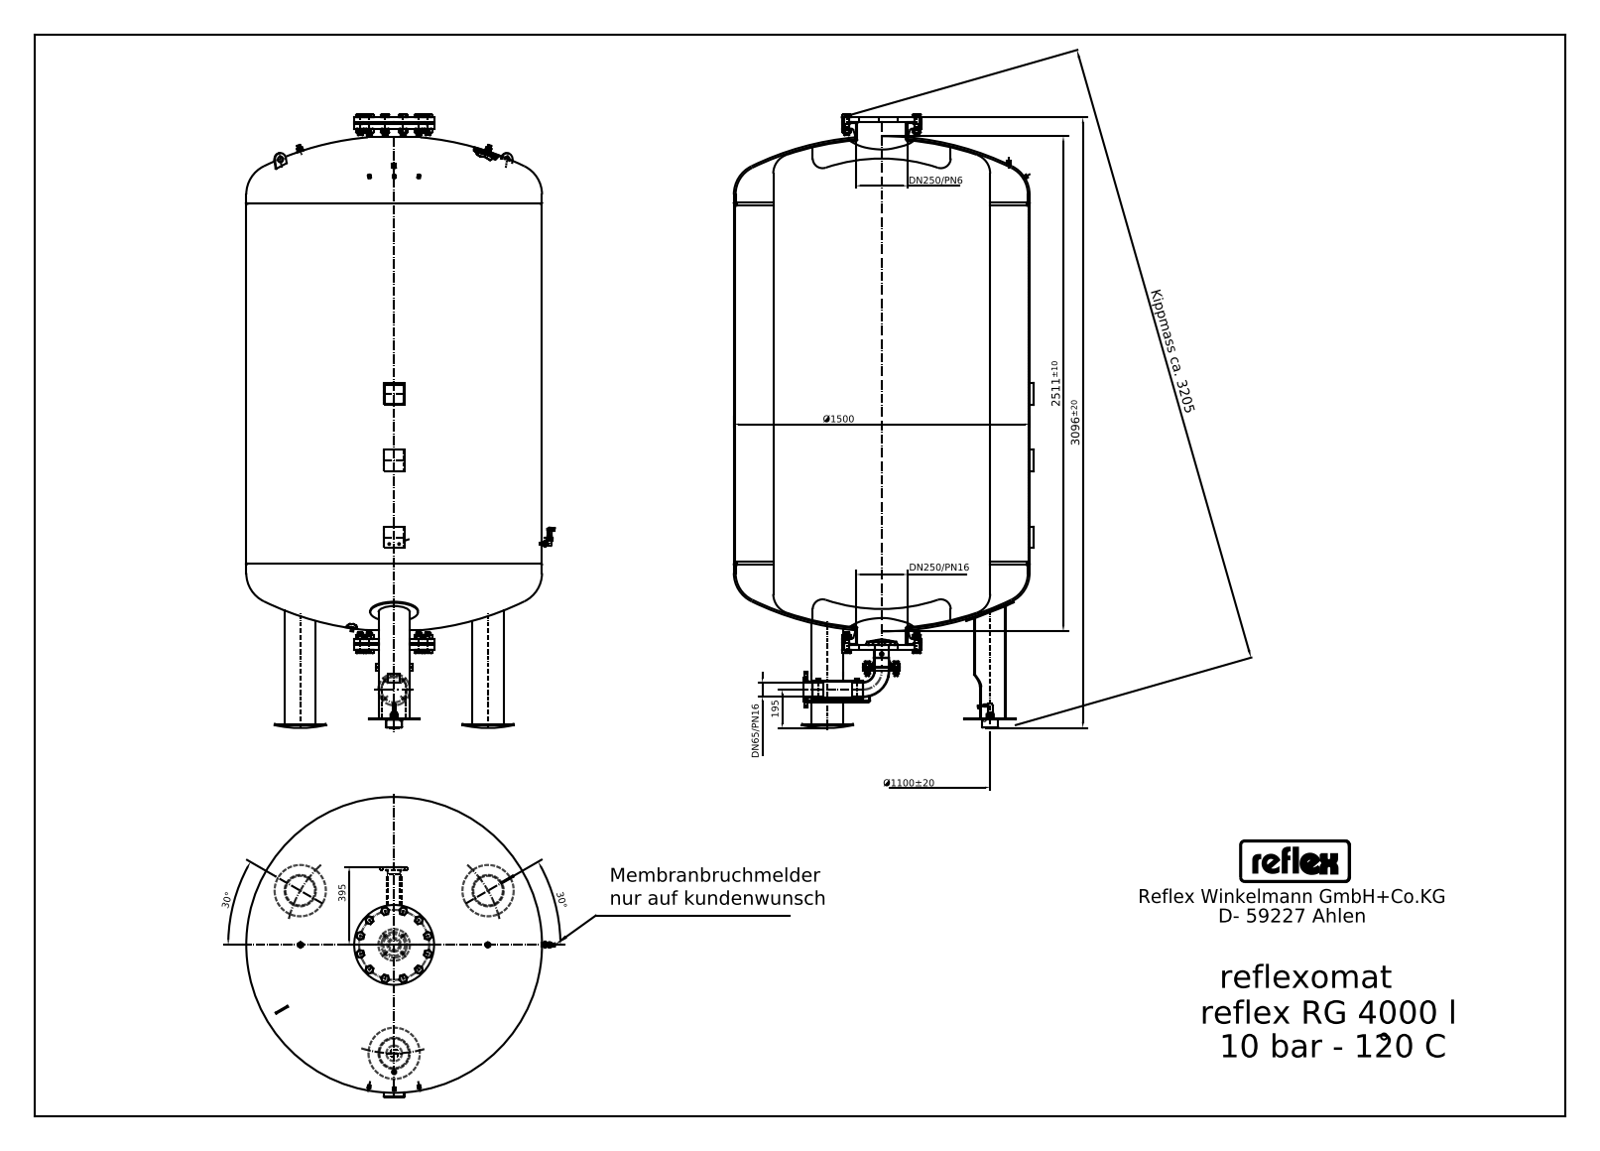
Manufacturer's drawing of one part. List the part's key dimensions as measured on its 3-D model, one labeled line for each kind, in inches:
STEP written by: Mechanical Desktop 2009 (CONFIG_CONTROL_DESIGN)
Units: inches
Bodies: 33 solids, 1142 faces (640 planar, 270 cylindrical, 232 other)
Overall size (bounding box): 121.693 × 61.654 × 59.843
Volume: 251 600 in³ · Surface area: 36 470 in²
Round holes (diameter × count): ⌀0.354 ×2, ⌀0.451 ×2, ⌀0.138 ×1, ⌀0.315 ×1, ⌀0.589 ×1, ⌀0.787 ×1, ⌀1.181 ×1, ⌀5.906 ×1, ⌀10.252 ×1
Round bosses / shafts (diameter × count): ⌀0.63 ×12, ⌀0.472 ×4, ⌀6.26 ×3, ⌀0.839 ×3, ⌀0.728 ×3, ⌀2.996 ×2, ⌀1.102 ×2, ⌀0.787 ×2
Partial cylindrical surfaces — rounded edges, fillets, slot ends (radius × count): R0.079 ×10, R0.039 ×5, R0.332 ×4, R0.133 ×3, R0.236 ×3, R0.118 ×2, R0.227 ×2, R0.398 ×2
Main face-to-face distances: 72.874, 0.866, 104.173, 1.063, 103.11, 15.118, 88.189, 15.315, 89.055, 16.181
Hole centre spacings: 32.298, 1.969, 3.74, 21.654, 25.394, 30.295, 37.238, 39.53
